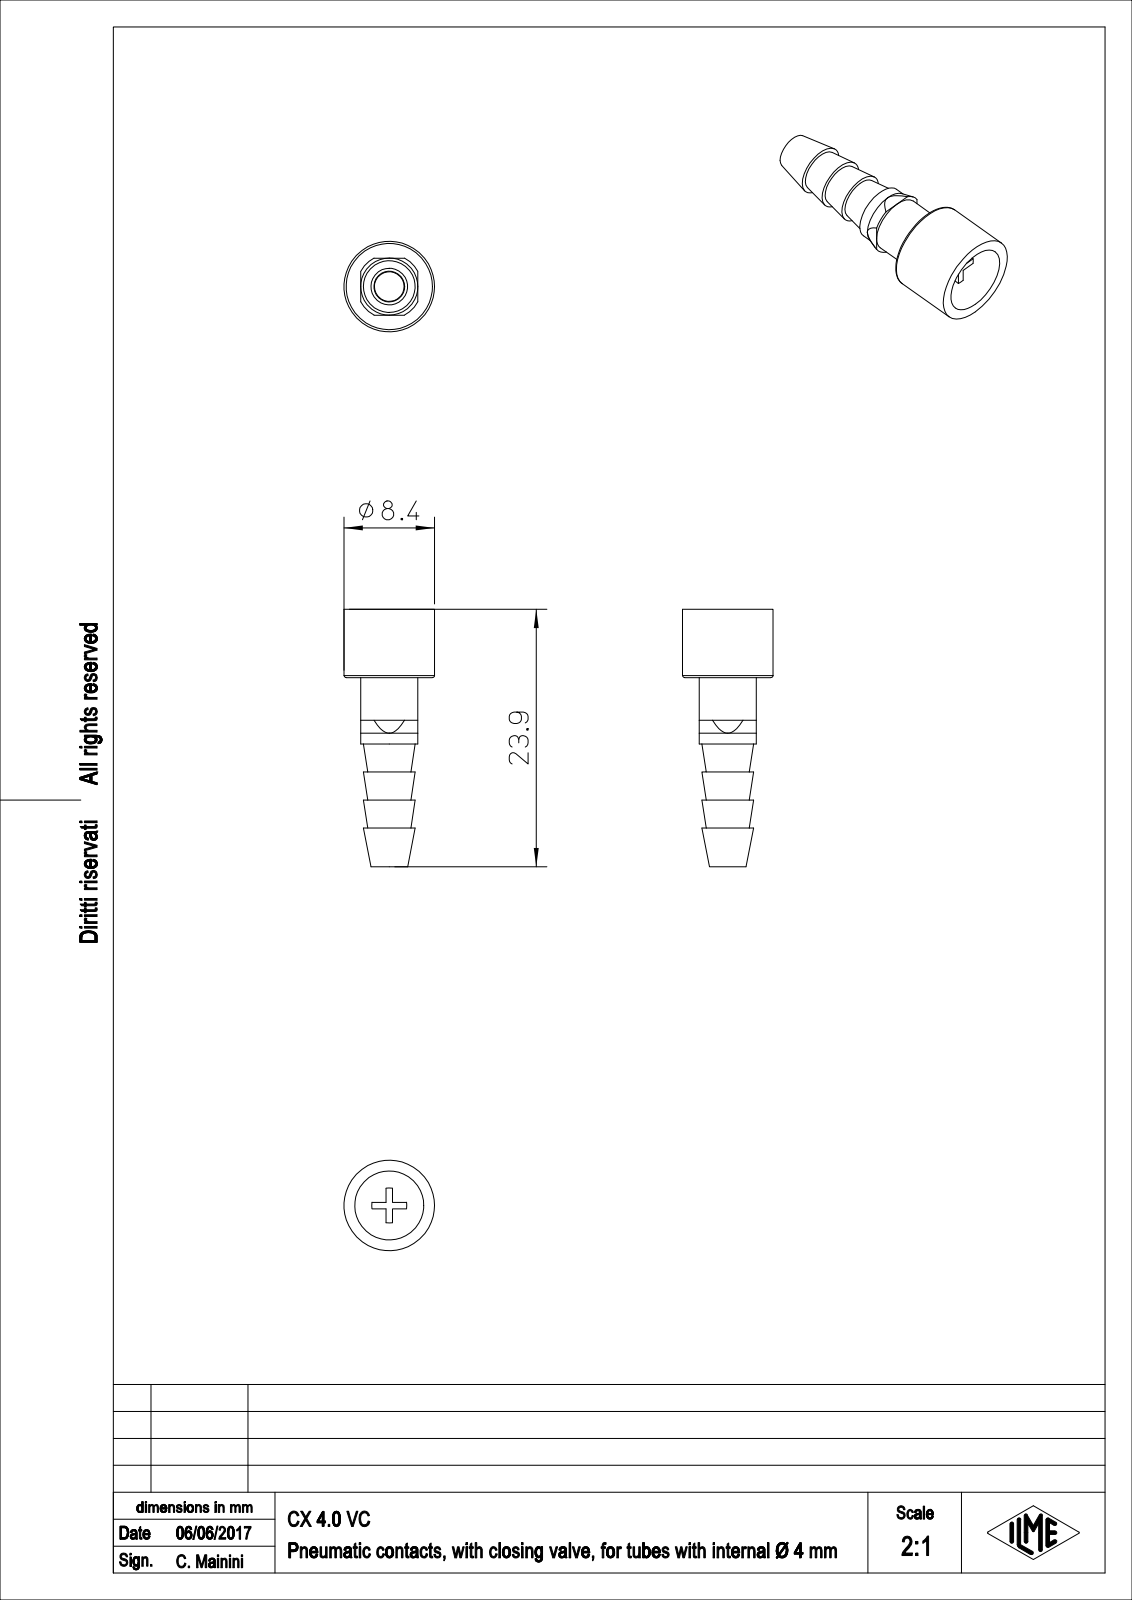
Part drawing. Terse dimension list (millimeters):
name: CX_4.0_VC
written by: PTC Creo Elements/Direct Modeling 19.0E 27-Jun-2016 (C) Parametric Technology GmbH (AUTOMOTIVE_DESIGN)
unit: mm
bodies: 1 solid, 71 faces (31 planar, 24 cylindrical, 16 other)
size: 23.9 × 8.4 × 8.4
volume: 337 mm³; area: 898 mm²
holes: 1× ⌀2.85, 1× ⌀4.84, 1× ⌀6.4
bosses: 1× ⌀8.4, 1× ⌀5.3, 1× ⌀2.75
rounds: 1× R1.62
face distances: 1.05, 5.3, 6.35, 2.6, 0.6, 1.35, 6.65, 5.2, 7.4, 10.3
